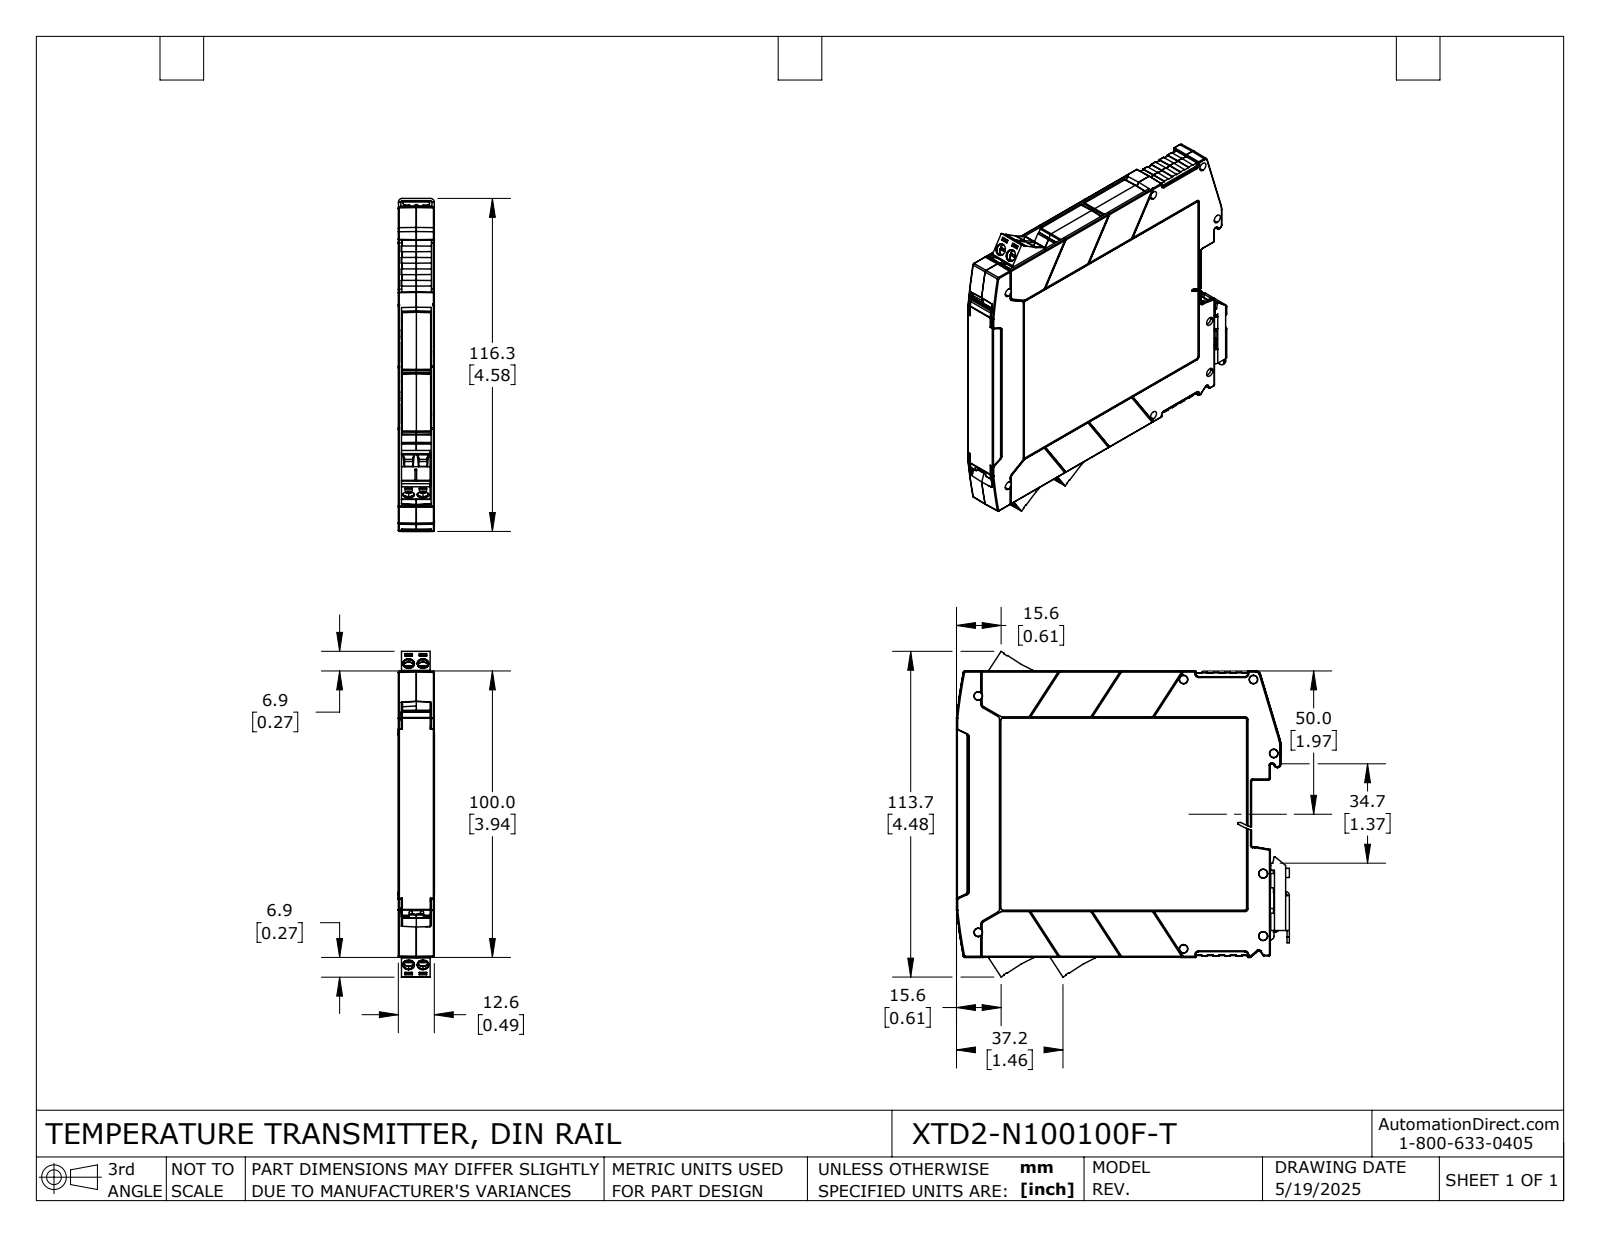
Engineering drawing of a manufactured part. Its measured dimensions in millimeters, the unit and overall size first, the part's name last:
Units: millimetres
Overall size (bounding box): 116.3 × 113.7 × 12.6
Round holes (diameter × count): ⌀1.6 ×6, ⌀2.8 ×6, ⌀3.9 ×6, ⌀4 ×6
Round bosses / shafts (diameter × count): ⌀4 ×6, ⌀2.5 ×6, ⌀1.5 ×2, ⌀1.3 ×2
Partial cylindrical surfaces — rounded edges, fillets, slot ends (radius × count): R0.2 ×89, R0.3 ×78, R0.5 ×71, R1 ×22, R0.1 ×20, R0.4 ×13, R0.2 ×12, R0.7 ×8
Main face-to-face distances: 1.2, 11.3, 12.5, 10.1, 1.1, 11.5, 10.2, 0.8, 5, 6.3
Hole centre spacings: 5, 11.8, 12.8, 18.1, 18.8
Volume: 39 490 mm³ · Surface area: 65 480 mm²
Bodies: 14 solids, 3337 faces (1910 planar, 596 cylindrical, 831 other)
Part name (STEP PRODUCT): XTD2-N100100F-T
STEP written by: SolidWorks 2024 (AUTOMOTIVE_DESIGN)
